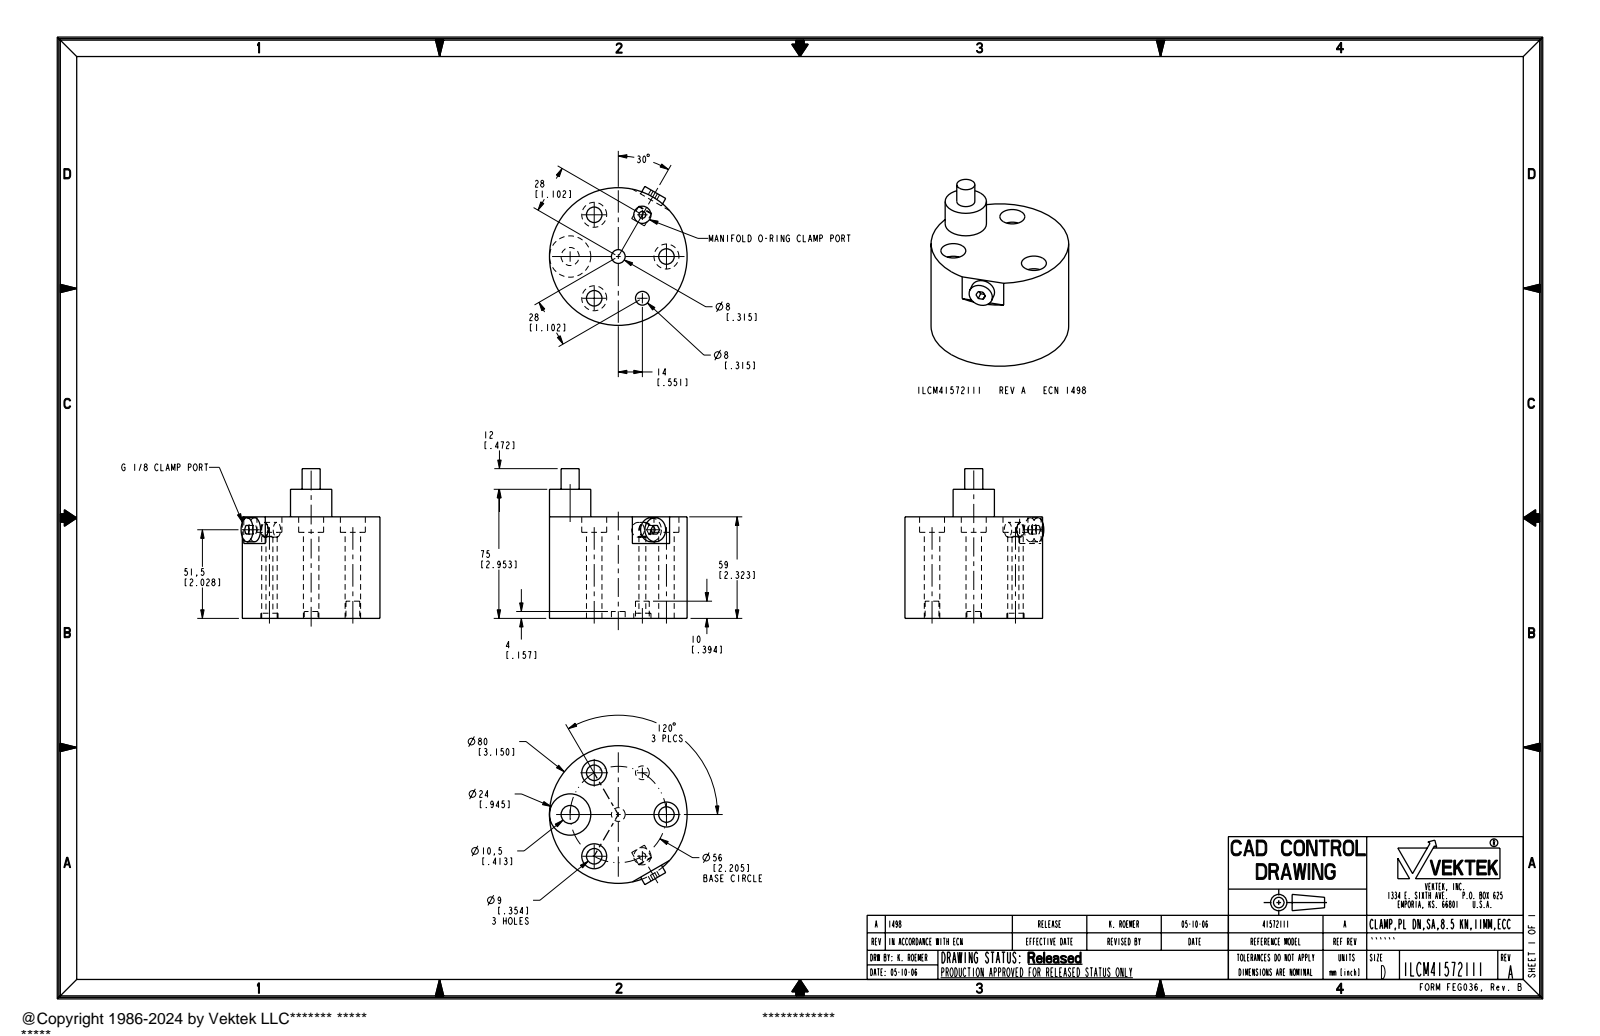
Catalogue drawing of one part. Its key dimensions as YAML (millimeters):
part_name: "ILCM41572111"
step_written_by: "PRO/ENGINEER BY PARAMETRIC TECHNOLOGY CORPORATION, 2004290 (AUTOMOTIVE_DESIGN_CC2)"
units: millimeters
bodies: {solids: 1, faces: 54, planar: 22, cylindrical: 30, other: 2}
overall_size: [87, 80.74, 80]
volume: 289025
surface_area: 33199
round_holes:
  - {diameter: 9, count: 3}
  - {diameter: 14.5, count: 3}
  - {diameter: 8, count: 2}
  - {diameter: 4, count: 1}
  - {diameter: 8.57, count: 1}
  - {diameter: 10, count: 1}
round_bosses_or_shafts:
  - {diameter: 80, count: 1}
  - {diameter: 24, count: 1}
  - {diameter: 14, count: 1}
  - {diameter: 10.5, count: 1}
face_to_face_distances: [59, 75, 16, 50, 9, 25, 5, 12, 7, 87]
hole_center_spacings: [28, 48.5, 56]
